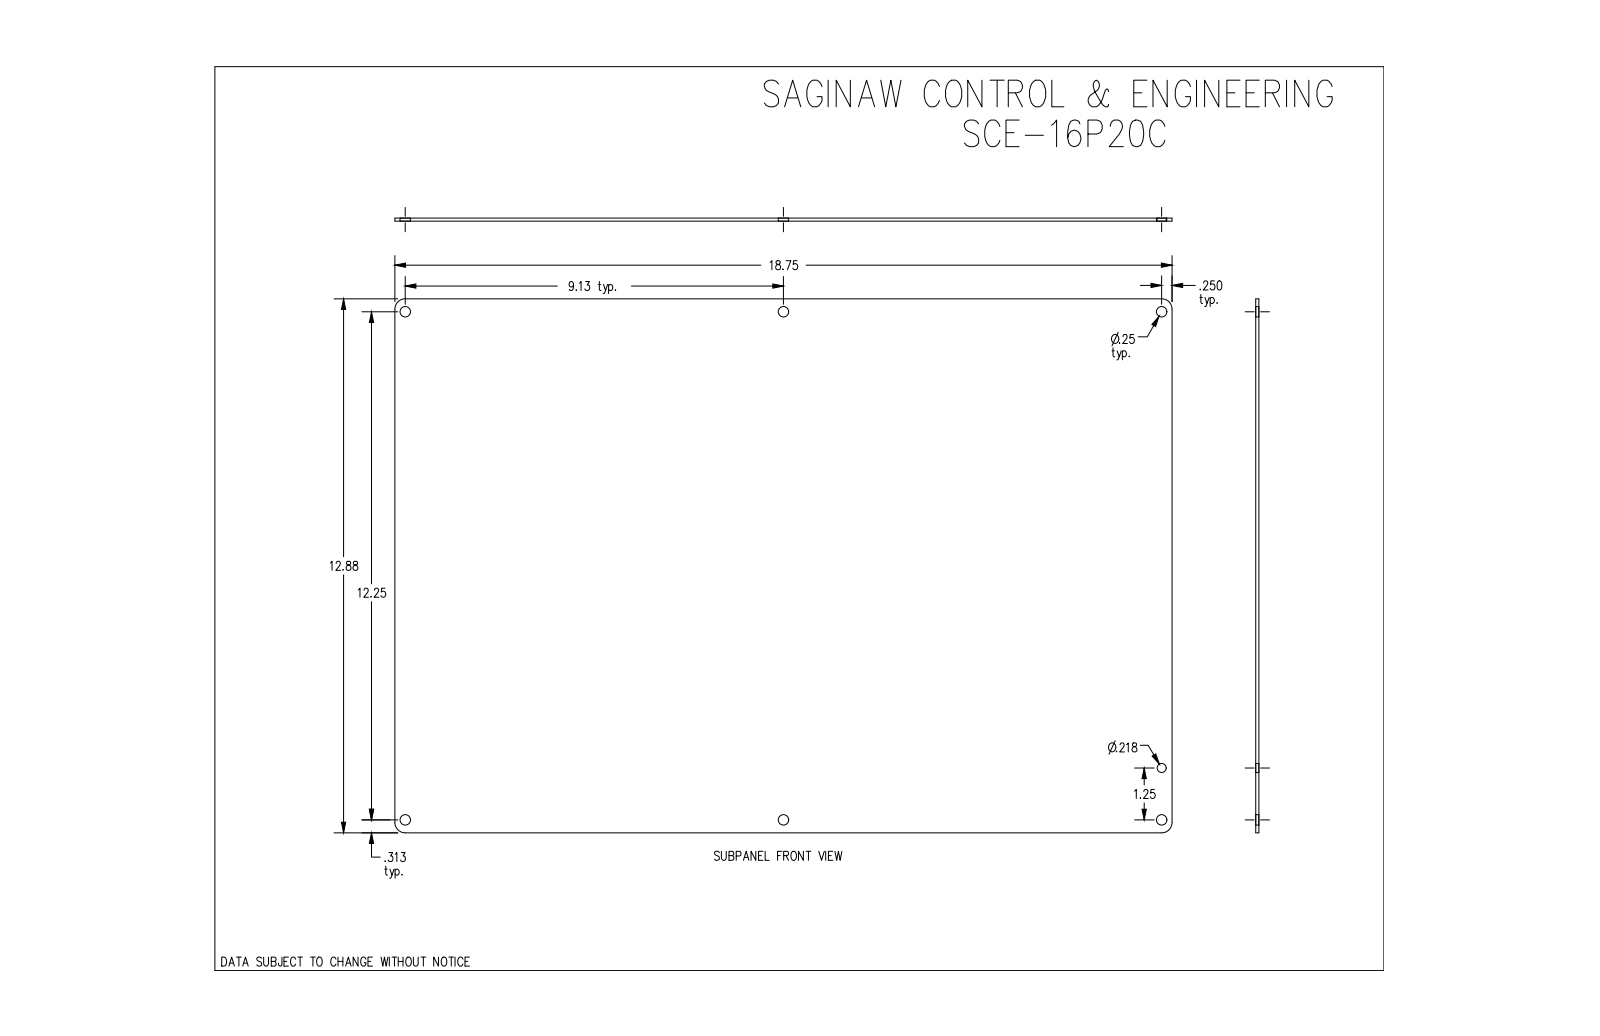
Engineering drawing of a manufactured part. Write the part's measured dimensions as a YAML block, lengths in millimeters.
part_name: "SCE-16P20C"
step_written_by: "SolidWorks 2019 (CONFIG_CONTROL_DESIGN)"
units: millimeters
bodies: {solids: 1, faces: 17, planar: 6, cylindrical: 11, other: 0}
overall_size: [476.3, 327, 1.9]
volume: 296300
surface_area: 314300
round_holes:
  - {diameter: 6.4, count: 6}
  - {diameter: 5.5, count: 1}
partial_cylinders:
  - {radius: 6.4, count: 4}
face_to_face_distances: [1.9, 327, 476.3]
hole_center_spacings: [231.8, 388, 311.2, 463.6, 558.3, 31.8, 233.9, 279.4]
